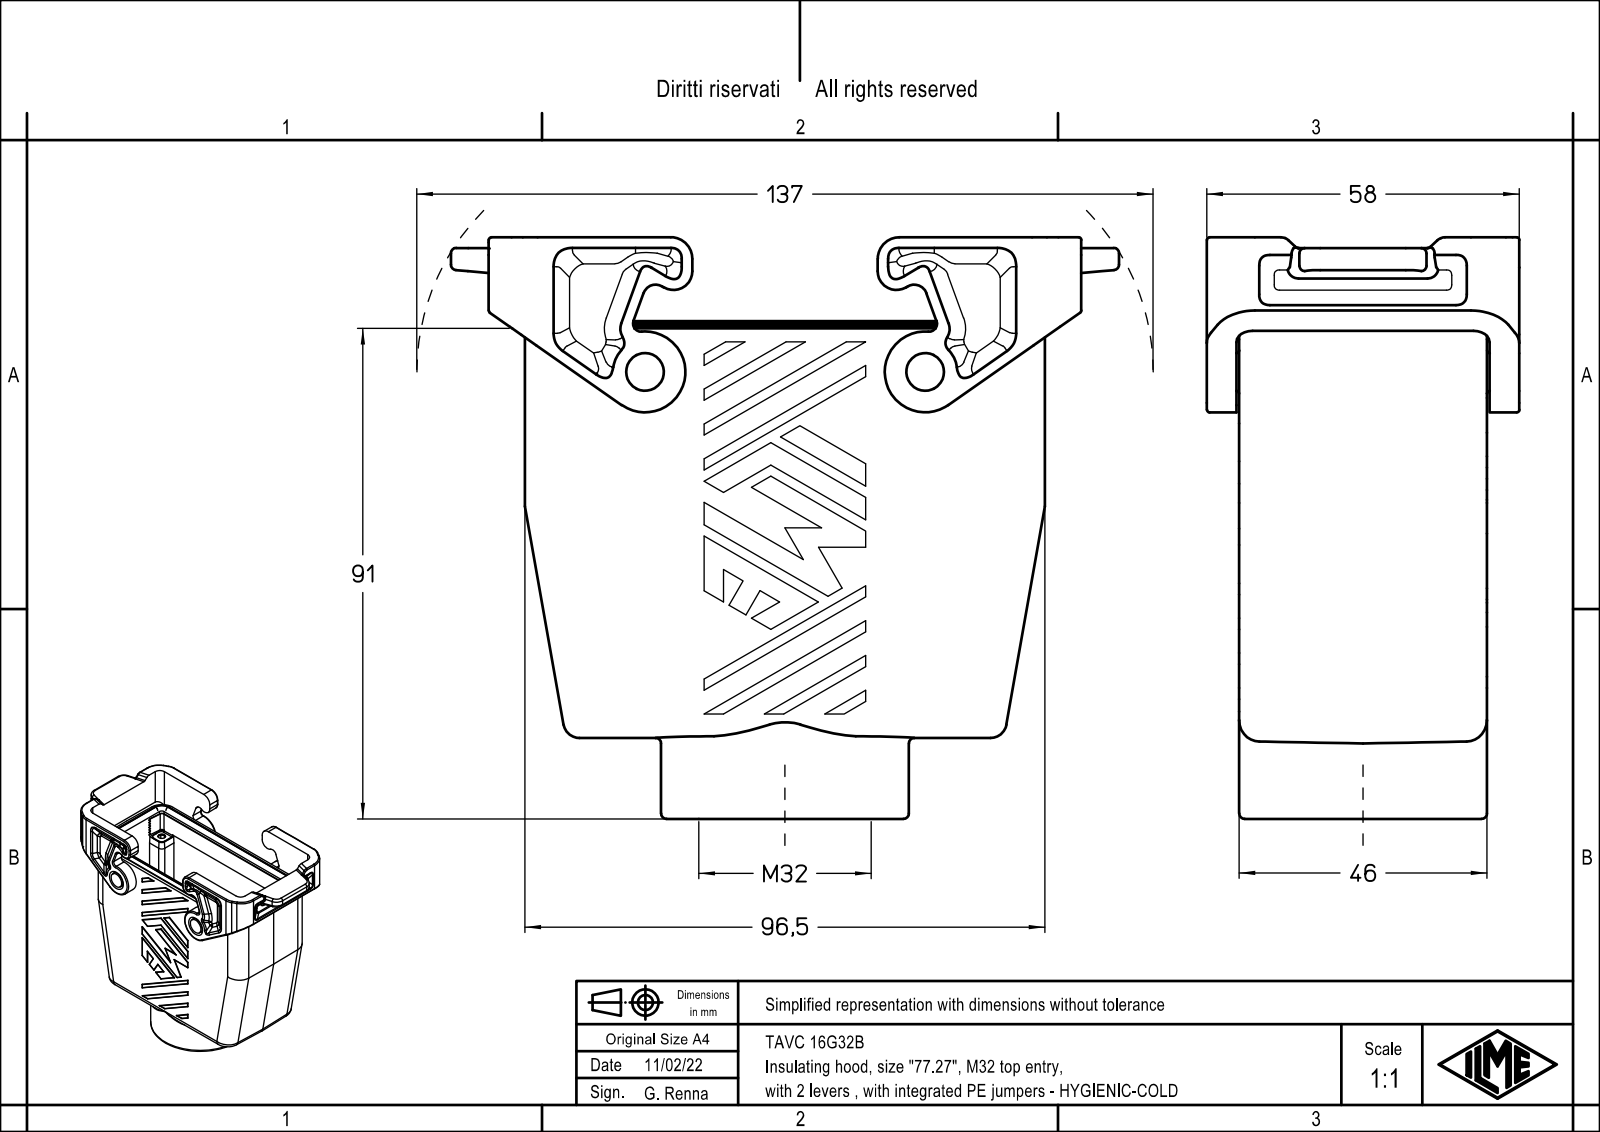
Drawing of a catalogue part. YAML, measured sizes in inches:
part_name: "TAVH 16 G32"
step_written_by: "Creo Elements/Direct Modeling 20.1B 02-Apr-2019 (C) Parametric Technology GmbH (AUTOMOTIVE_DESIGN)"
units: inches
bodies: {solids: 1, faces: 754, planar: 374, cylindrical: 318, other: 62}
overall_size: [4.882, 4.248, 2.283]
volume: 9.866
surface_area: 100.2
round_holes:
  - {diameter: 0.138, count: 4}
  - {diameter: 1.102, count: 1}
  - {diameter: 1.205, count: 1}
round_bosses_or_shafts:
  - {diameter: 0.276, count: 2}
  - {diameter: 1.811, count: 1}
partial_cylinders:
  - {radius: 0.006, count: 88}
  - {radius: 0.079, count: 20}
  - {radius: 0.118, count: 20}
  - {radius: 0.059, count: 18}
  - {radius: 0.039, count: 16}
  - {radius: 0.051, count: 12}
  - {radius: 0.236, count: 8}
  - {radius: 0.276, count: 8}
face_to_face_distances: [0.213, 1.598, 1.386, 1.811, 0.02, 0.232, 1.618, 1.831, 0.217, 0.236]
hole_center_spacings: [1.615, 1.063, 3.051, 3.231]
